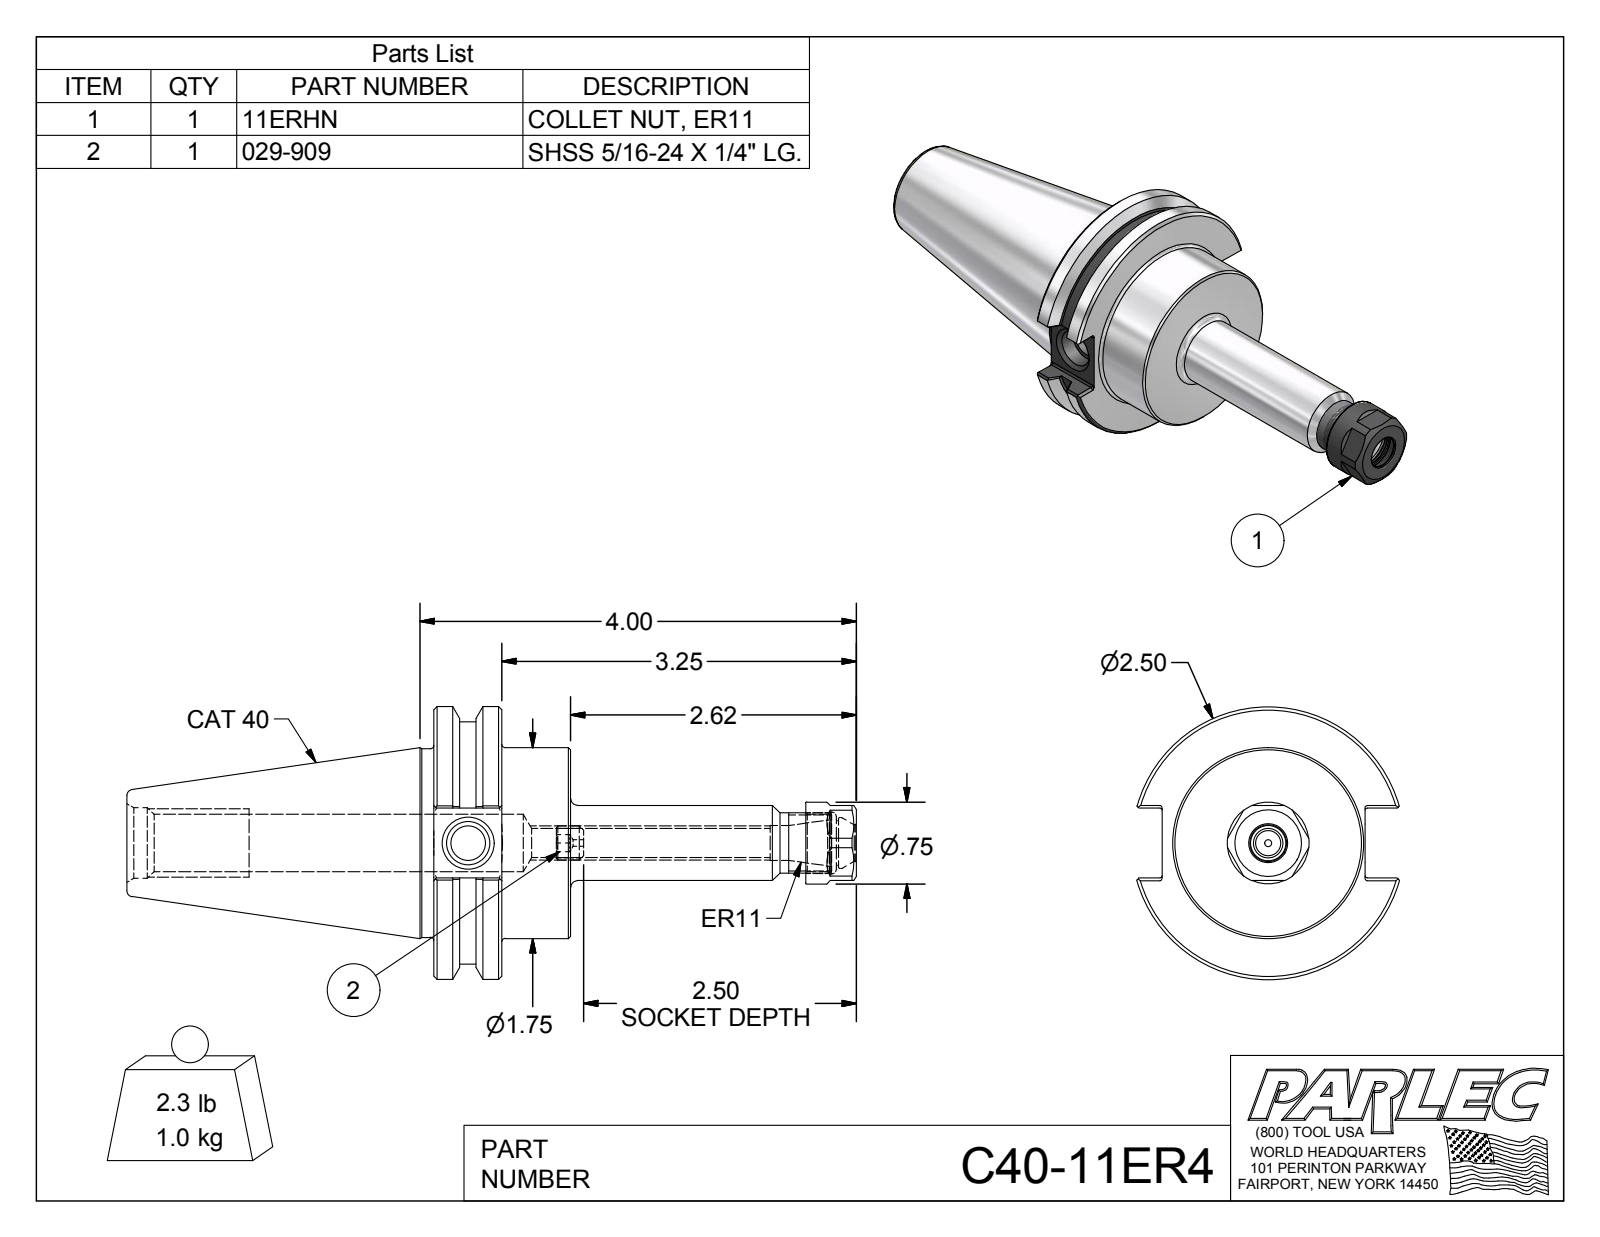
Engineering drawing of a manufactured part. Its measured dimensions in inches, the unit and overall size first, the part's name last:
Units: inches
Overall size (bounding box): 6.687 × 2.5 × 2.406
Round holes (diameter × count): ⌀0.06 ×1, ⌀0.267 ×1, ⌀0.315 ×1, ⌀0.32 ×1, ⌀0.335 ×1, ⌀0.399 ×1, ⌀0.465 ×1, ⌀0.525 ×1, ⌀0.527 ×1, ⌀0.565 ×1, ⌀0.648 ×1
Round bosses / shafts (diameter × count): ⌀2.5 ×1, ⌀2.219 ×1, ⌀1.75 ×1, ⌀1.73 ×1, ⌀0.75 ×1, ⌀0.688 ×1, ⌀0.551 ×1, ⌀0.313 ×1
Partial cylindrical surfaces — rounded edges, fillets, slot ends (radius × count): R0.02 ×12
Main face-to-face distances: 1.255, 0.625, 0.63, 0.64, 1.86, 3.875, 3.25, 2.62, 2.812, 3.437
Volume: 8.352 in³ · Surface area: 45.35 in²
Bodies: 3 solids, 148 faces (63 planar, 35 cylindrical, 50 other)
Part name (STEP PRODUCT): C40-11ER4; C40-11ER4-1; 11ERHN; 029-909
STEP written by: Autodesk Inventor 2012 (AUTOMOTIVE_DESIGN)
